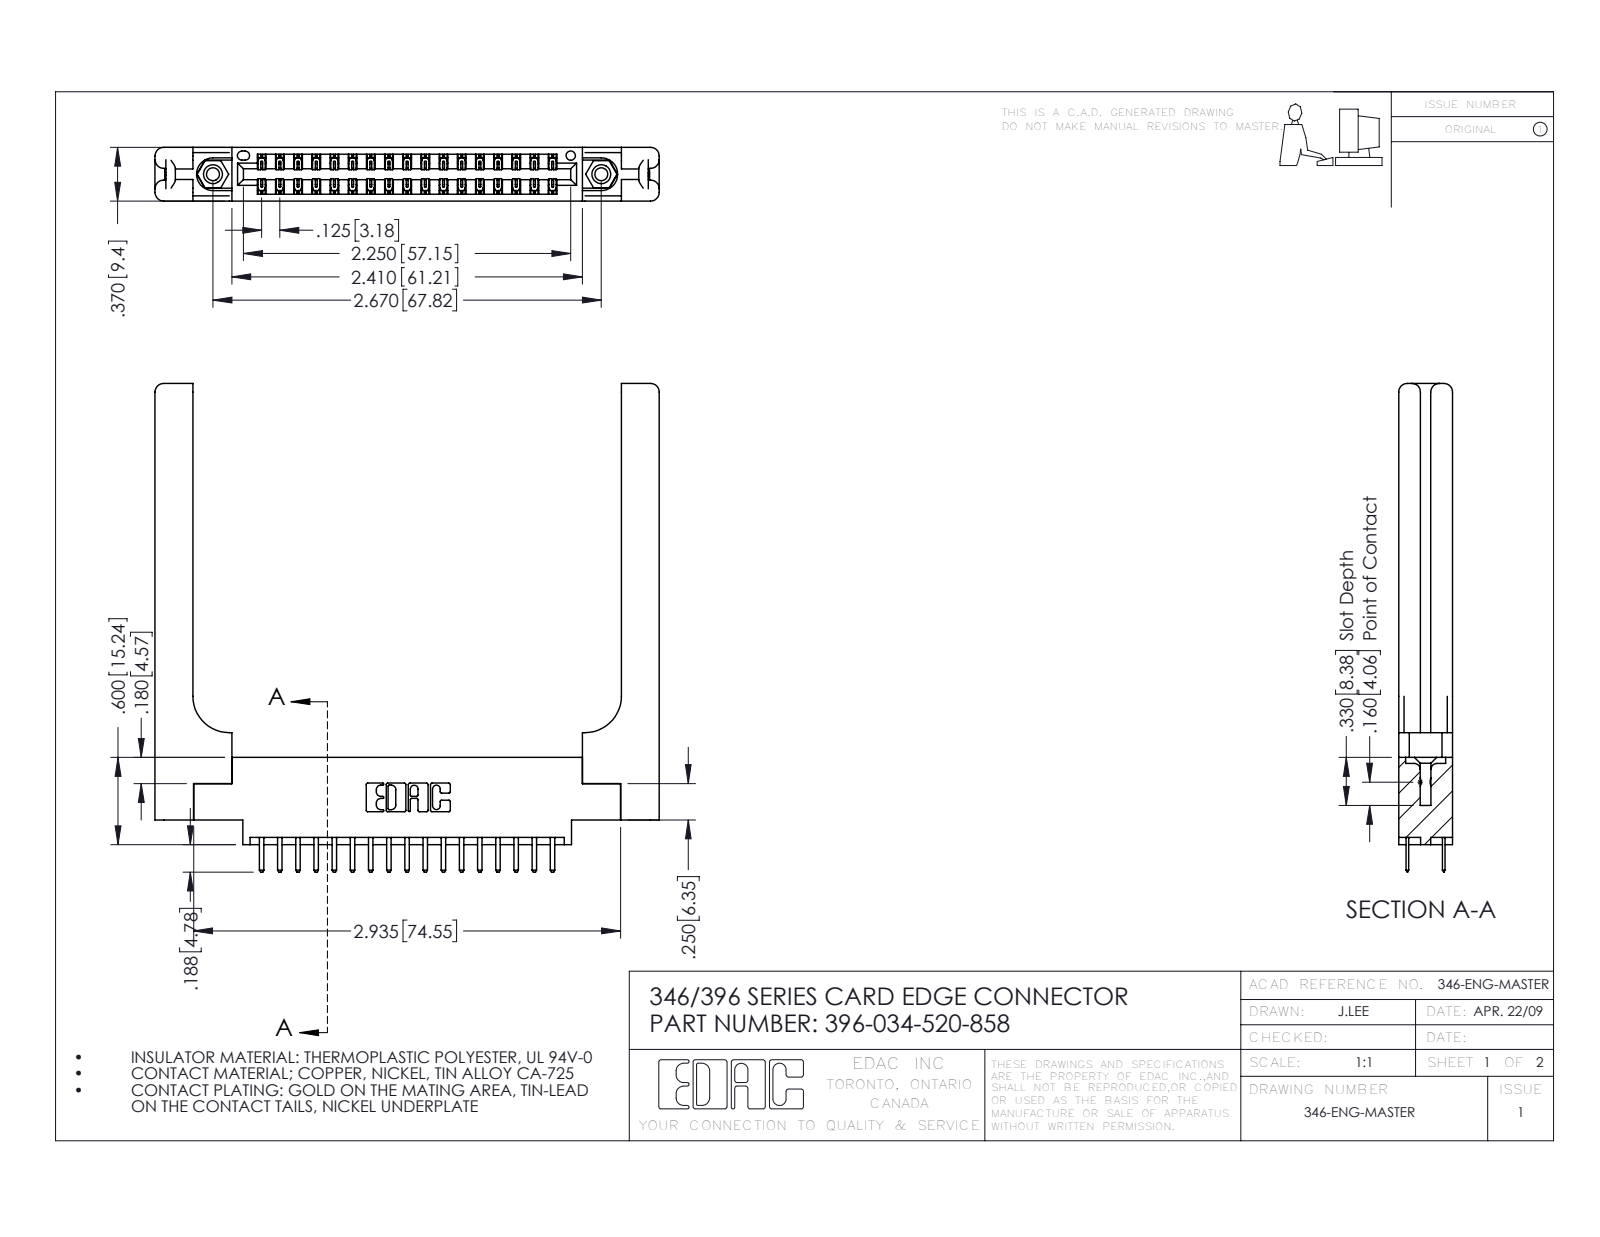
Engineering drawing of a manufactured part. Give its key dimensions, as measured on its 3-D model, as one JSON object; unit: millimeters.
{"part_name": "396-034-520-858; 346-220-058_345-220-058; 346 Part_0.170 Offset - 0.156 Dia-TH; 345-292-001_345-293-120 (+1 more)", "step_written_by": "SolidWorks 2016 (CONFIG_CONTROL_DESIGN)", "units": "millimeters", "bodies": {"solids": 39, "faces": 2286, "planar": 1486, "cylindrical": 740, "other": 60}, "overall_size": [88, 85.3, 9.4], "volume_mm3": 15700, "surface_area_mm2": 16030, "round_holes": [[2.3, 2], [3.2, 2], [4, 2], [1.6, 1]], "round_bosses_or_shafts": [[3.9, 2]], "partial_cylinders_radius": [[0.2, 51], [0.3, 38], [0.3, 22], [1.5, 16], [0.2, 6], [0.8, 6], [0.7, 3], [0.4, 2]], "face_to_face_distances": [9.4, 3.8, 1.8, 3.8, 1.2, 8.2, 6.4, 2.6, 5.6, 4.4], "hole_center_spacings": [6.2, 62.6, 67.8]}
